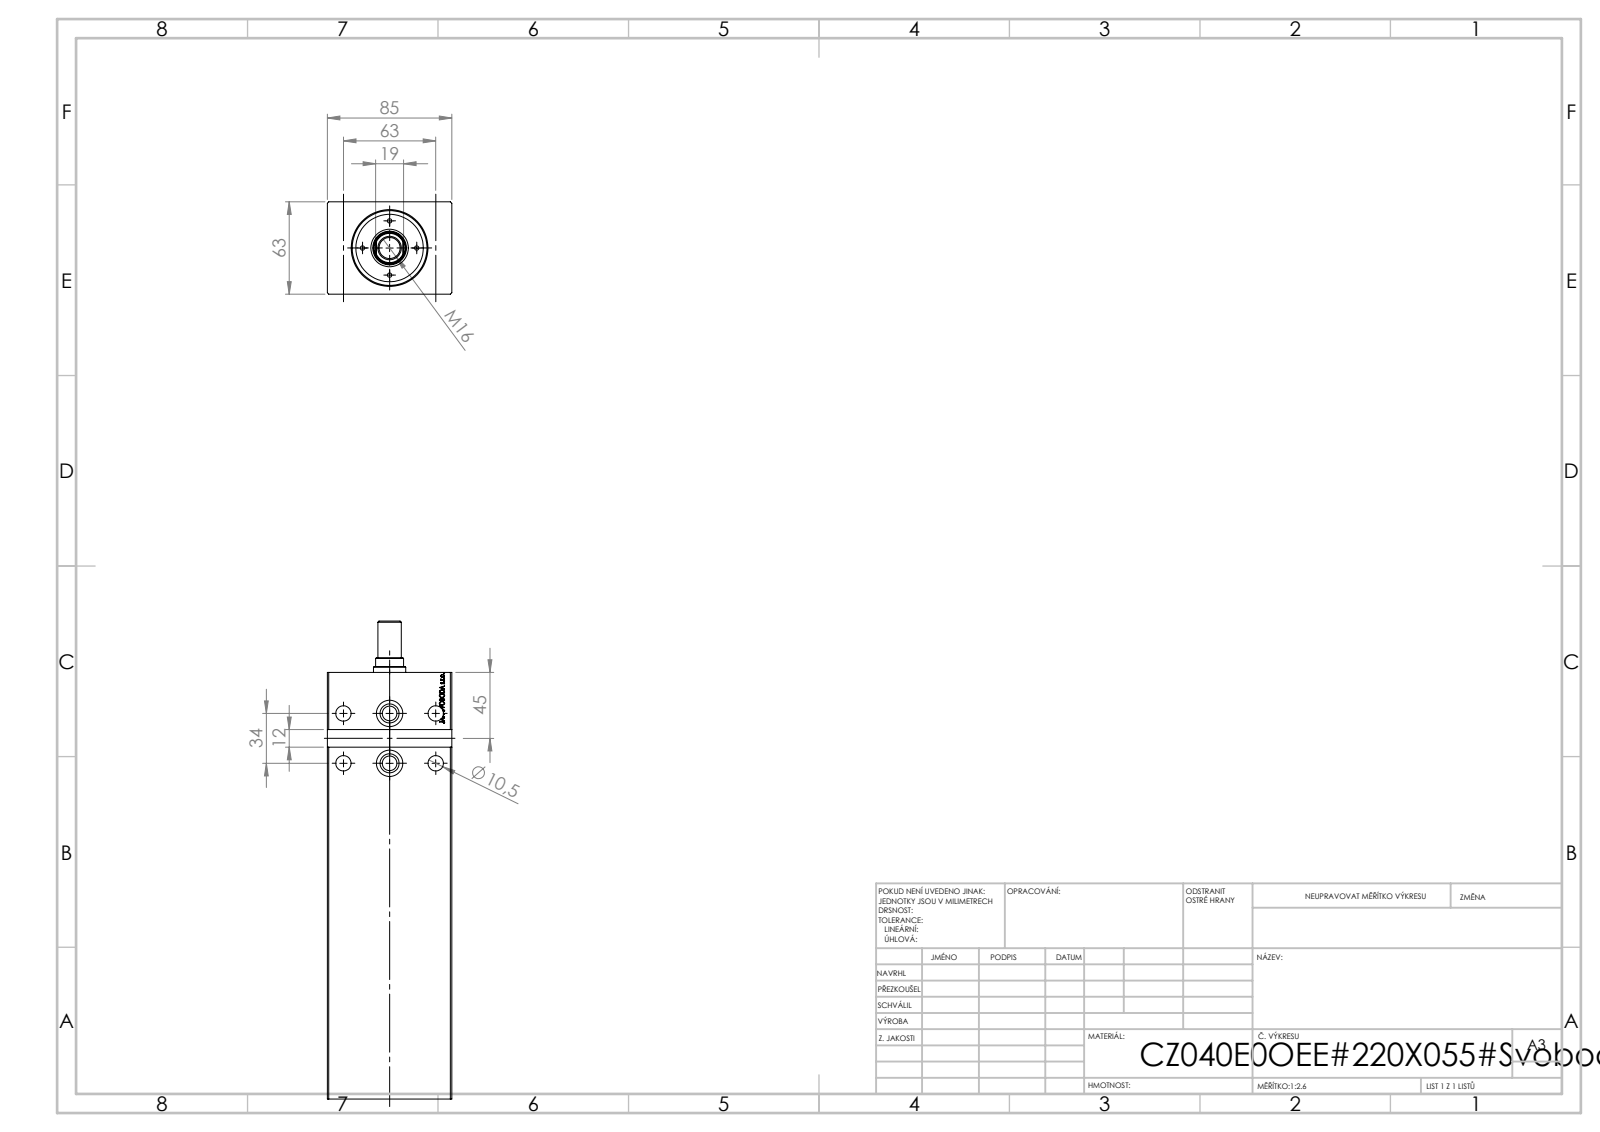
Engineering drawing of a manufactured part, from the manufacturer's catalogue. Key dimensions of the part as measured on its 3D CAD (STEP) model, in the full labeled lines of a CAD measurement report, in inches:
STEP written by: SolidWorks 2019 (CONFIG_CONTROL_DESIGN)
Units: inches
Bodies: 1 solid, 779 faces (383 planar, 30 cylindrical, 366 other)
Overall size (bounding box): 11.457 × 3.346 × 2.48
Volume: 71.89 in³ · Surface area: 216.6 in²
Round holes (diameter × count): ⌀0.413 ×4, ⌀0.315 ×2, ⌀0.394 ×2, ⌀0.709 ×2, ⌀1.417 ×1, ⌀1.575 ×1, ⌀2.008 ×1
Round bosses / shafts (diameter × count): ⌀0.512 ×2
Main face-to-face distances: 2.48, 3.346, 11.457, 10.854, 0.602, 0.079, 2.402, 11.449, 0.594, 4.064
Hole centre spacings: 1.24, 1.825, 1.339, 2.48, 2.819, 0.616, 0.742, 1.197
